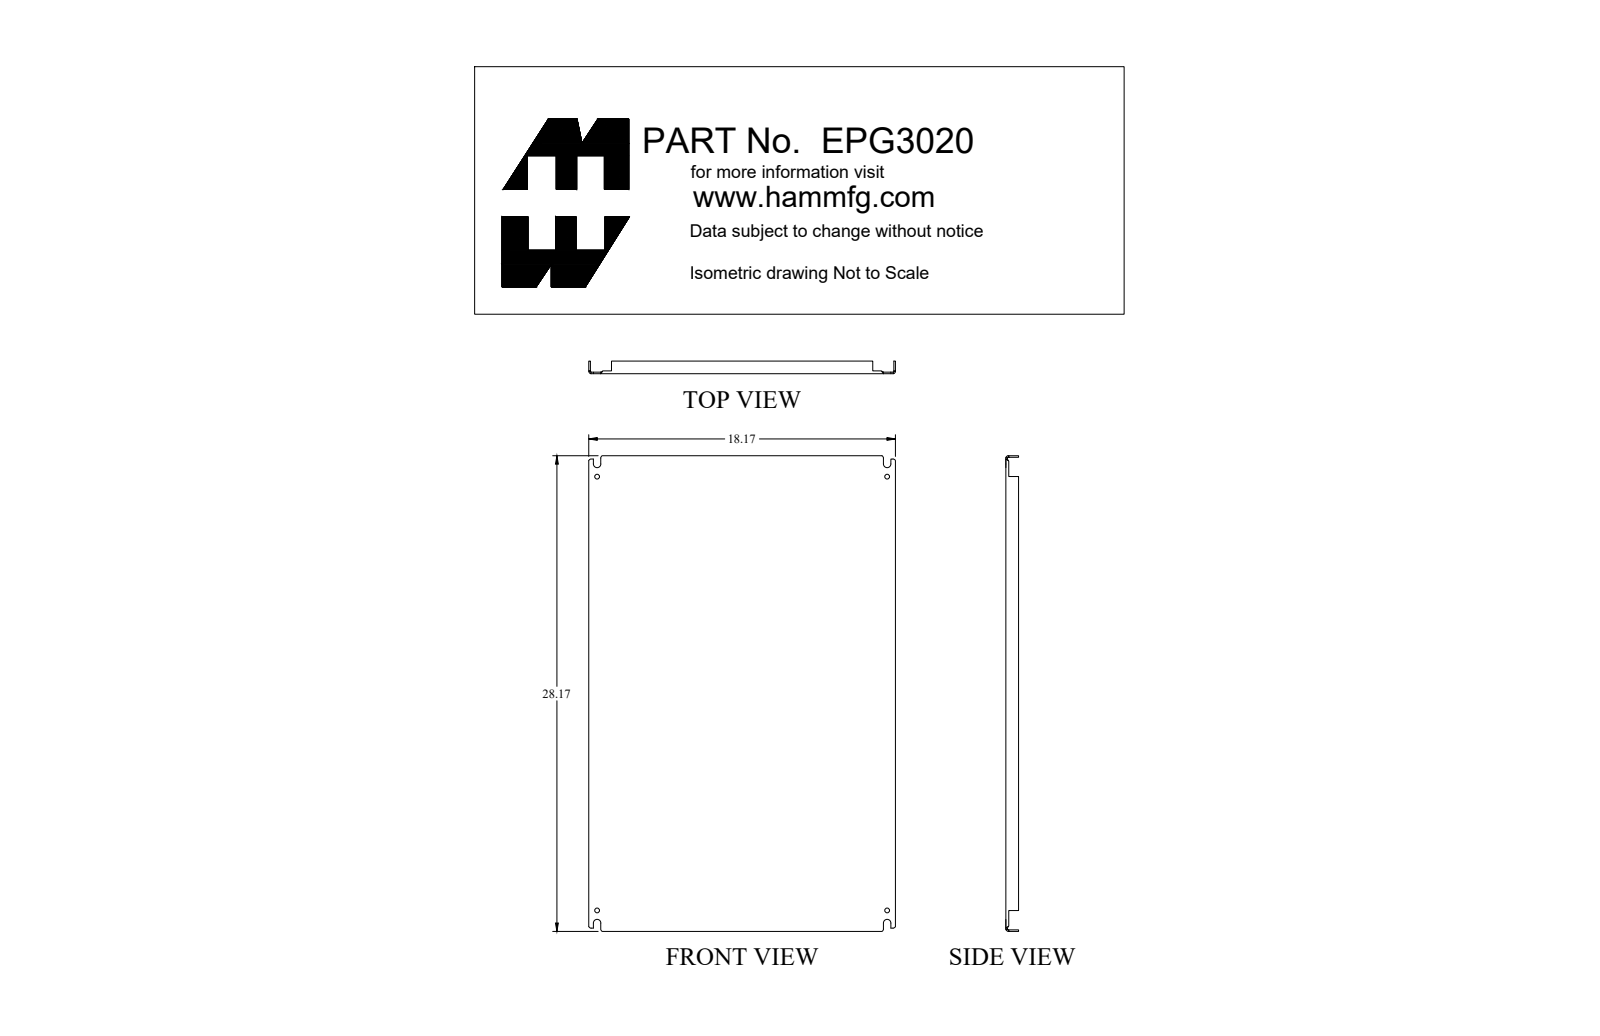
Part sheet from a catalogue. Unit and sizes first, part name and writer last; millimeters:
Units: millimetres
Overall size (bounding box): 715.5 × 461.5 × 19.1
Round holes (diameter × count): ⌀7.1 ×4
Partial cylindrical surfaces — rounded edges, fillets, slot ends (radius × count): R1.2 ×4, R1.6 ×4, R3.6 ×4, R5.6 ×4
Main face-to-face distances: 2.4, 459.1, 713.1, 456.7, 461.5, 710.7, 715.5, 19.1, 16.6, 4.3
Hole centre spacings: 436.6, 652.5, 785.1
Volume: 873 100 mm³ · Surface area: 730 300 mm²
Bodies: 1 solid, 128 faces (74 planar, 38 cylindrical, 16 other)
Part name (STEP PRODUCT): EPG3020
STEP written by: SolidWorks 2018 (AUTOMOTIVE_DESIGN)
